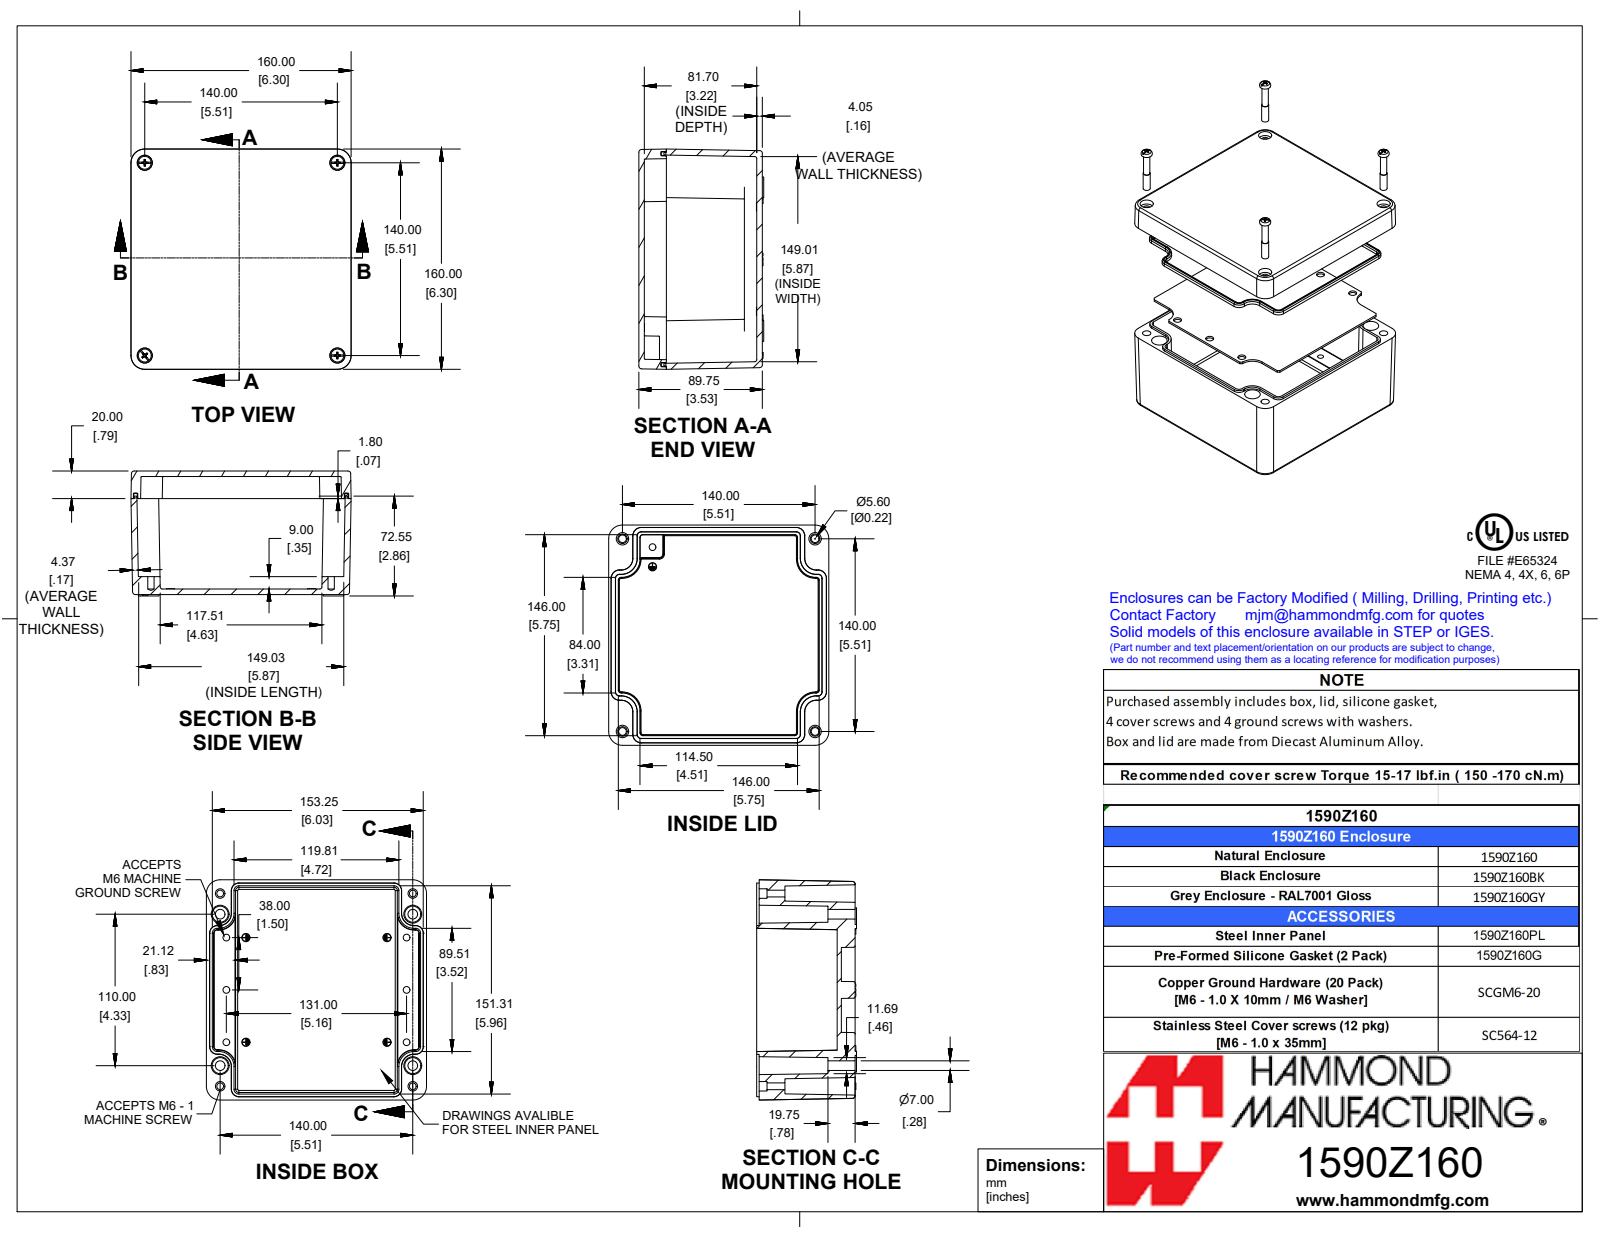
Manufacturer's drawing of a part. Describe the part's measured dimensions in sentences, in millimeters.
The part is named "1590Z160GY". Its 3-D file was written by "SolidWorks 2019 (CONFIG_CONTROL_DESIGN)". It is 7 solids with 824 faces: 471 planar, 133 cylindrical and 220 other. Overall it measures 160 by 160 by 90.8 millimeters. Its volume is 557 200 cubic millimeters and its surface area 240 500 square millimeters. Round holes: 11 of diameter 4.9, 5 of diameter 5.5, 4 of diameter 5.6, 4 of diameter 6.9, 4 of diameter 7, 4 of diameter 9. Round bosses or shafts: 5 of diameter 6, 4 of diameter 5.9, 4 of diameter 5.3. Partial cylindrical surfaces (rounded edges, fillets, slot ends): 20 of radius 1, 12 of radius 0.5, 8 of radius 1.4, 8 of radius 2, 8 of radius 10, 6 of radius 0.3, 4 of radius 1.5. The main face-to-face distances are 4.4, 89.7, 85.8, 4, 4, 81.7, 85.7, 160, 155.6, 69.7. The hole center spacings are 140, 14.2, 15, 17.6, 25.3, 32.3, 37.1, 38.
